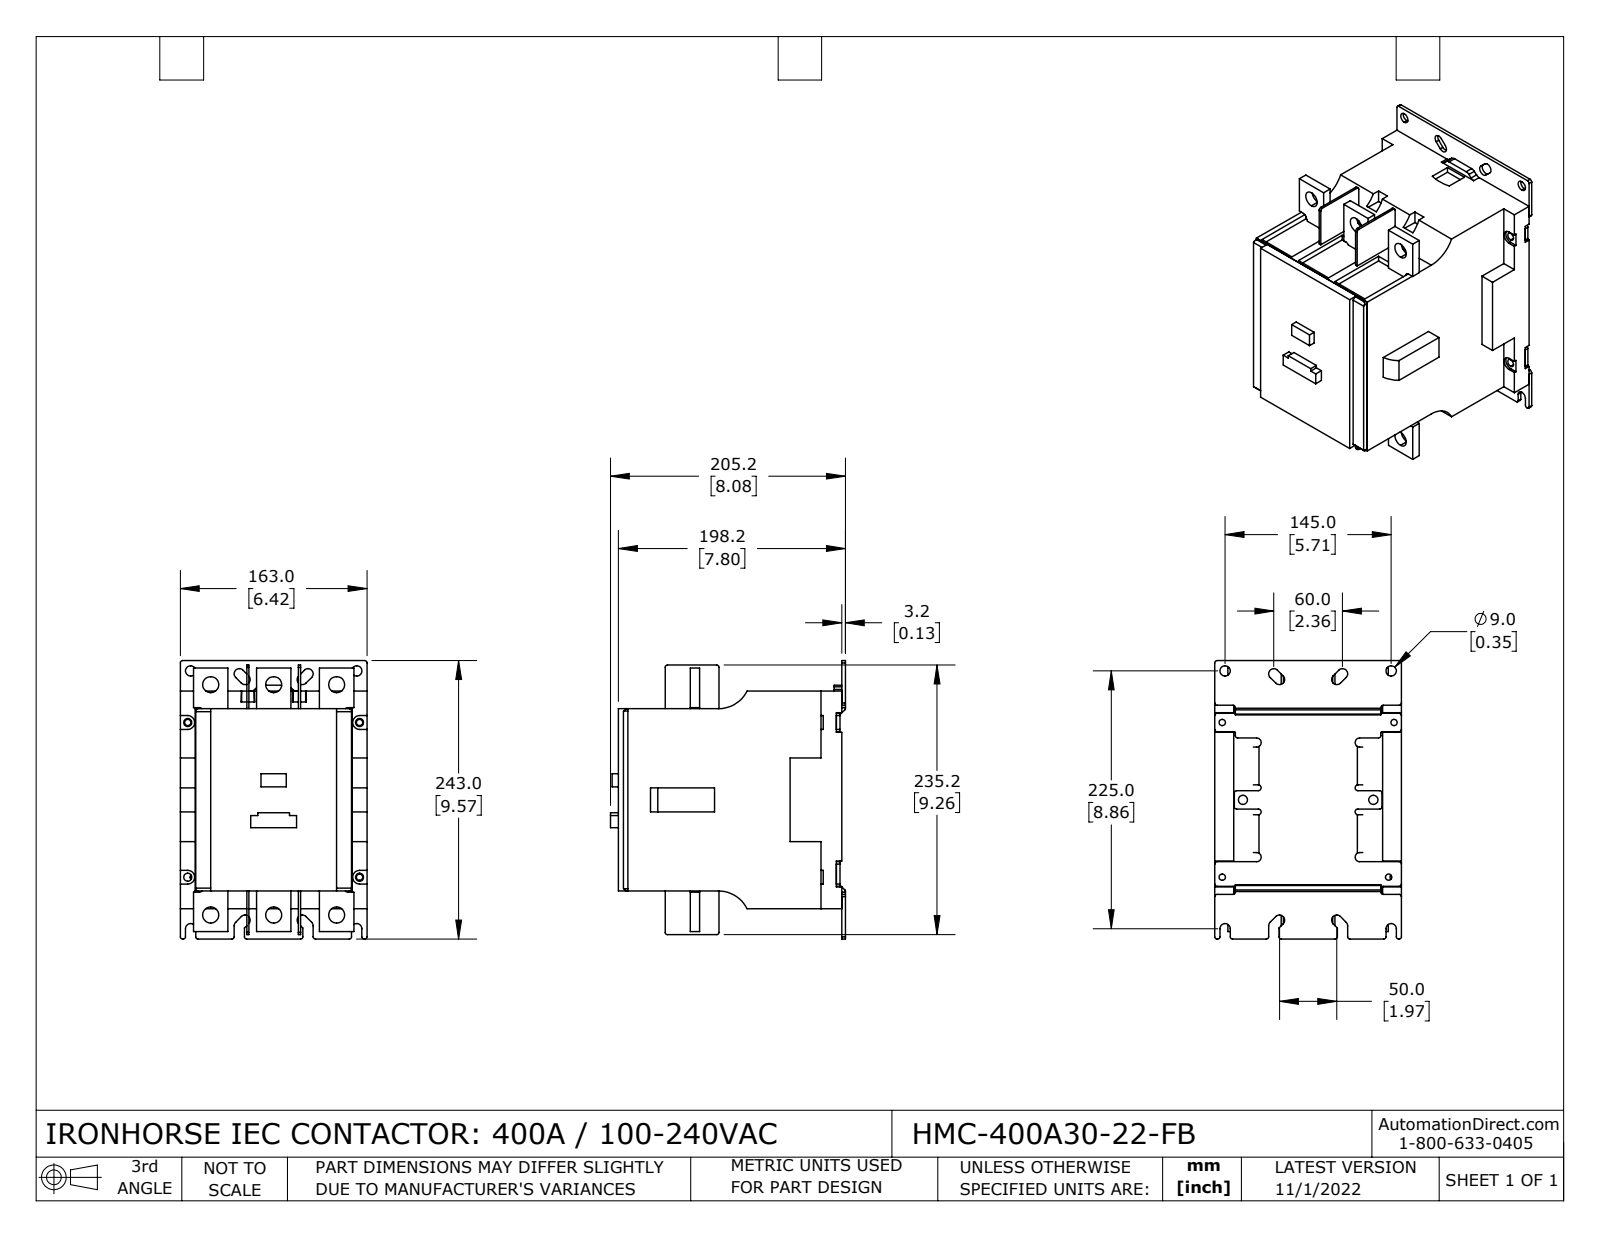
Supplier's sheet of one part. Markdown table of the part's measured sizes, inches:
| quantity | value |
| --- | --- |
| part name | HMC-400A30-22-FB |
| STEP written by | SolidWorks 2021 (CONFIG_CONTROL_DESIGN) |
| units | inches |
| bodies | 9 solids, 491 faces (308 planar, 145 cylindrical, 38 other) |
| overall size | 9.567 × 8.079 × 6.417 |
| volume | 292.1 in³ |
| surface area | 551.8 in² |
| round holes (diameter × count) | 0.551 × 6, 0.276 × 4, 0.217 × 3, 0.315 × 2, 0.354 × 2 |
| partial cylindrical surfaces (radius × count) | 0.079 × 52, 0.177 × 10, 0.039 × 4, 0.098 × 4, 0.157 × 4, 0.197 × 4, 0.205 × 4, 0.236 × 4 |
| main face-to-face distances | 7.165, 0.126, 0.185, 5.394, 7.35, 0.059, 7.677, 7.492, 0.327, 7.291 |
| hole center spacings | 1.519, 2.165, 2.751, 3.226, 3.957, 4.548, 5.28, 5.835 |
